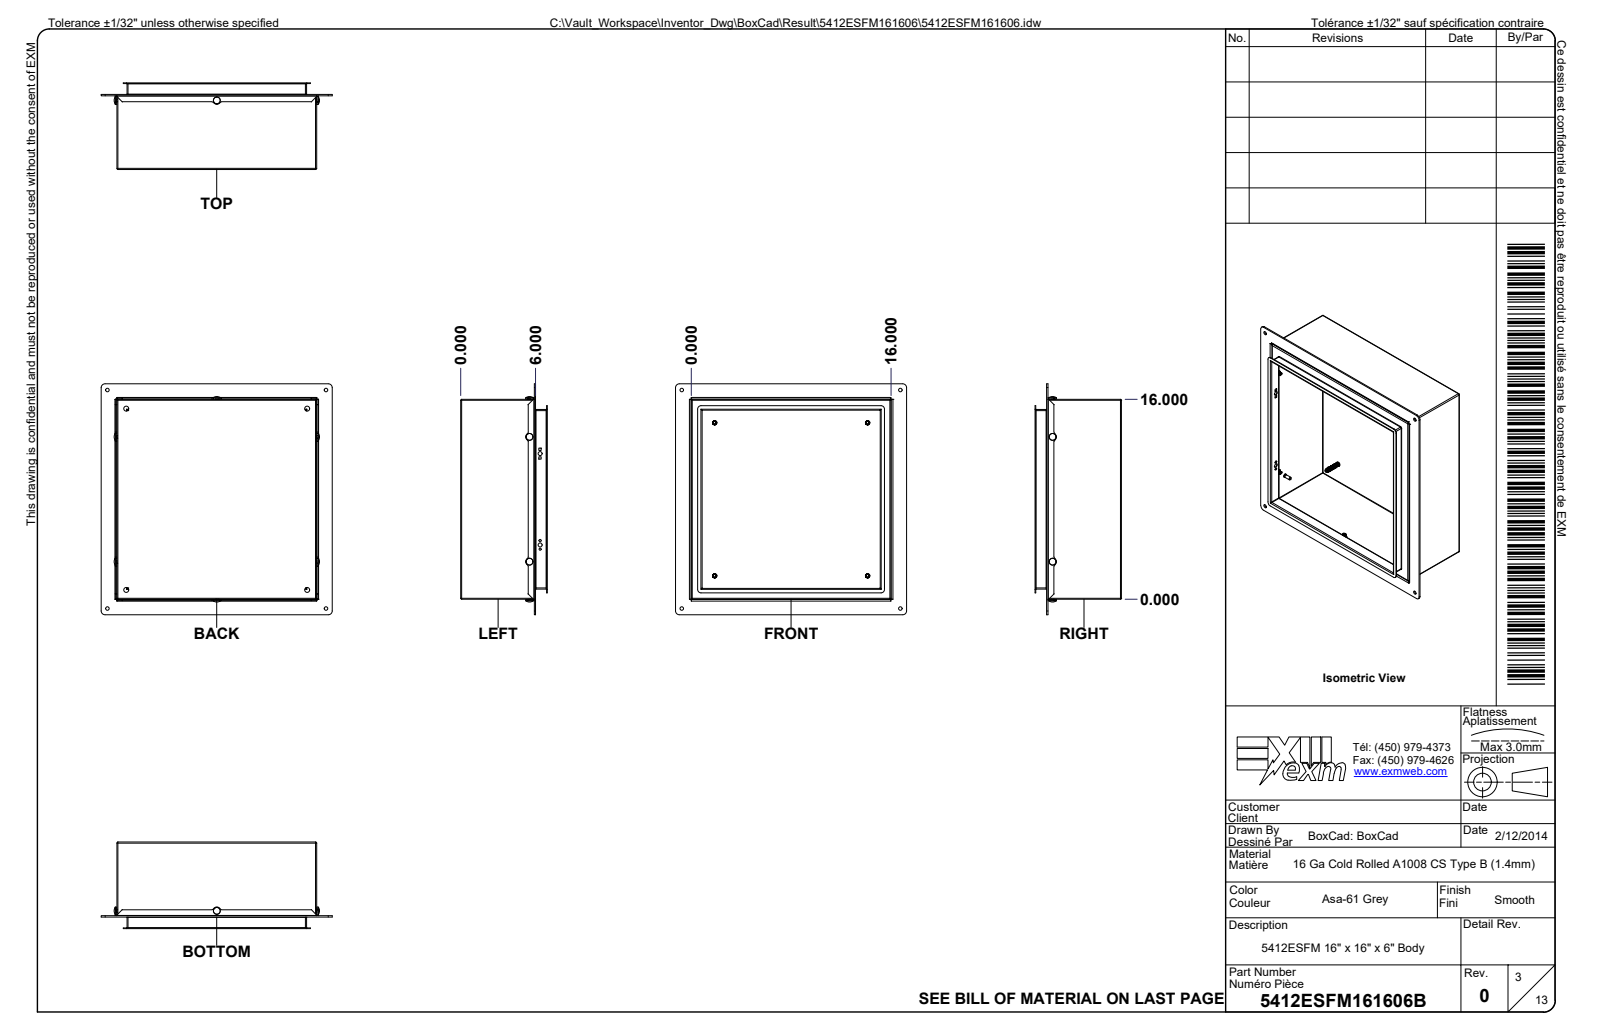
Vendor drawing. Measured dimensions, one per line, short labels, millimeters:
name: 5412ESFM161606; 5412ESFM161606B; 5412ESFM161606B-P; STK-Q-16005 (+8 more)
written by: Autodesk Inventor 2024 (AUTOMOTIVE_DESIGN)
unit: mm
bodies: 87 solids, 9256 faces (2473 planar, 2584 cylindrical, 4199 other)
size: 469.9 × 469.9 × 185.7
volume: 1 581 000 mm³; area: 1 914 000 mm²
holes: 24× ⌀4.2, 11× ⌀7.4, 11× ⌀8, 10× ⌀5.1, 9× ⌀0.8, 8× ⌀1.1, 7× ⌀5, 7× ⌀6.8, 5× ⌀7.9, 4× ⌀4.5, 4× ⌀6.9, 4× ⌀9.9
bosses: 24× ⌀6, 11× ⌀5.9, 9× ⌀0.8, 8× ⌀1, 7× ⌀9.5, 4× ⌀18.2, 4× ⌀7.9, 4× ⌀6.7
rounds: 275× R0.5, 107× R0.3, 98× R0.2, 93× R1, 30× R0.4, 28× R0.8, 26× R0.3, 24× R2.1
face distances: 1.3, 179.9, 405.1, 178.5, 181.2, 23.5, 22.2, 156.3, 157.7, 26.2
hole spacings: 50, 25, 340.9, 383.7, 408.2, 75, 185.5, 100
